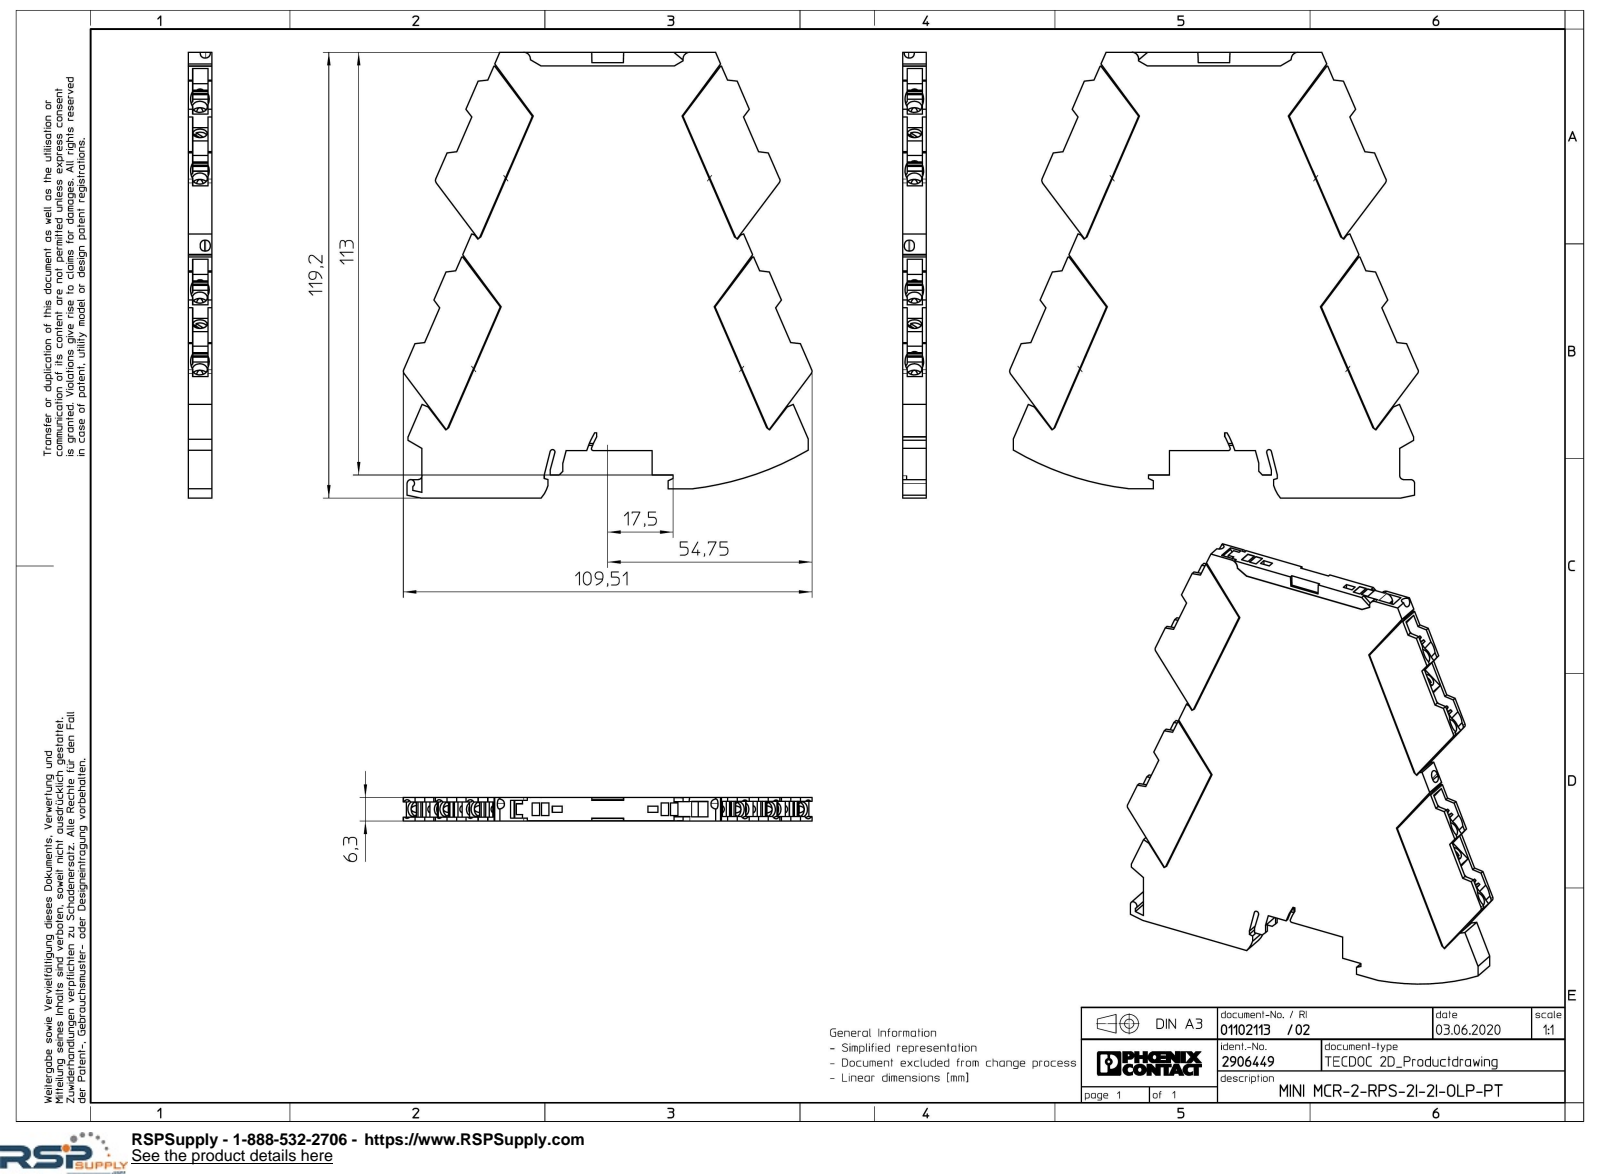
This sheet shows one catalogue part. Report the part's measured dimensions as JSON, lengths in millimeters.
{"part_name": "MINI_ANALOG_PRO-SOCKEL-select; FASTCON_PRO-SET-PT-select.1; MINI_ANALOG_PRO-PT-select", "step_written_by": "Creo Elements/Direct Modeling 20.1A 29-Sep-2018 (C) Parametric Technology GmbH (AUTOMOTIVE_DESIGN)", "units": "millimeters", "bodies": {"solids": 5, "faces": 1234, "planar": 1080, "cylindrical": 125, "other": 29}, "overall_size": [119.2, 109.51, 6.3], "volume_mm3": 58791, "surface_area_mm2": 35575, "round_holes": [[2, 8], [4, 8], [3.3, 4], [3.8, 4]], "round_bosses_or_shafts": [[3, 4]], "partial_cylinders_radius": [[3.5, 16], [1.5, 8], [1, 6], [0.2, 5], [1.15, 4], [1.18, 4], [1.8, 3], [0.5, 1]], "face_to_face_distances": [6.3, 2.65, 5.35, 2.55, 37.57, 2.75, 1.65, 4.72, 0.32, 0.31], "hole_center_spacings": [37.56, 18.2, 6.3, 11.45, 13.05, 5.15, 6.75, 11.9]}
